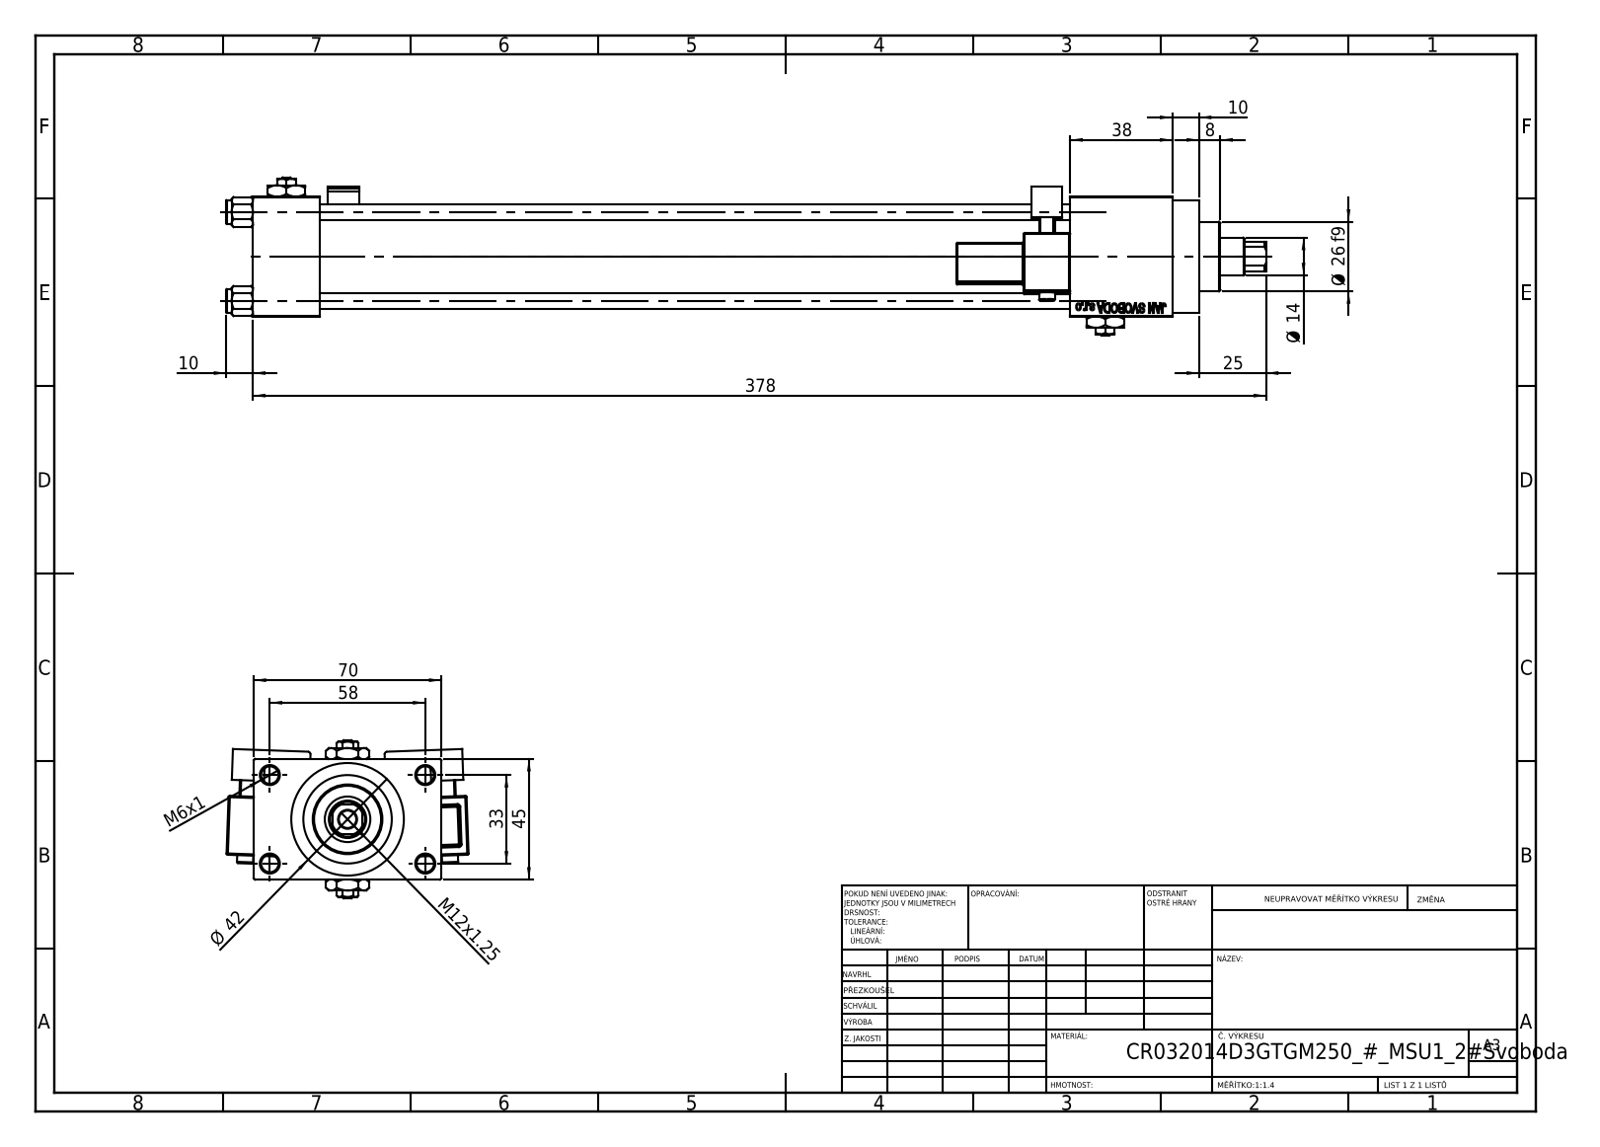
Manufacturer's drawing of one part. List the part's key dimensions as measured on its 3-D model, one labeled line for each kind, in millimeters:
Part name (STEP PRODUCT): V215CR_VCP_D; V215CR_D_TYCINKA; V215CR_MSU; Zatka_pro_OIL_PORT (+3 more)
STEP written by: SolidWorks 2019 (CONFIG_CONTROL_DESIGN)
Units: millimetres
Bodies: 15 solids, 1345 faces (602 planar, 149 cylindrical, 594 other)
Overall size (bounding box): 388 × 90.31 × 59
Volume: 411 532 mm³ · Surface area: 166 101 mm²
Round holes (diameter × count): ⌀6.5 ×5, ⌀6 ×4, ⌀7 ×2, ⌀13.16 ×2, ⌀20 ×2, ⌀14 ×1, ⌀17 ×1, ⌀24 ×1, ⌀32 ×1, ⌀33 ×1
Round bosses / shafts (diameter × count): ⌀9 ×4, ⌀6 ×2, ⌀42 ×1, ⌀38 ×1, ⌀26 ×1
Partial cylindrical surfaces — rounded edges, fillets, slot ends (radius × count): R0.5 ×48, R1 ×2, R2.5 ×2, R4 ×2, R6.5 ×1
Main face-to-face distances: 45, 25, 12.5, 280, 3, 57.5, 305, 318, 38, 70
Hole centre spacings: 12.4, 23.48, 33.2, 33.37, 35.35, 45.6, 56.35, 33
